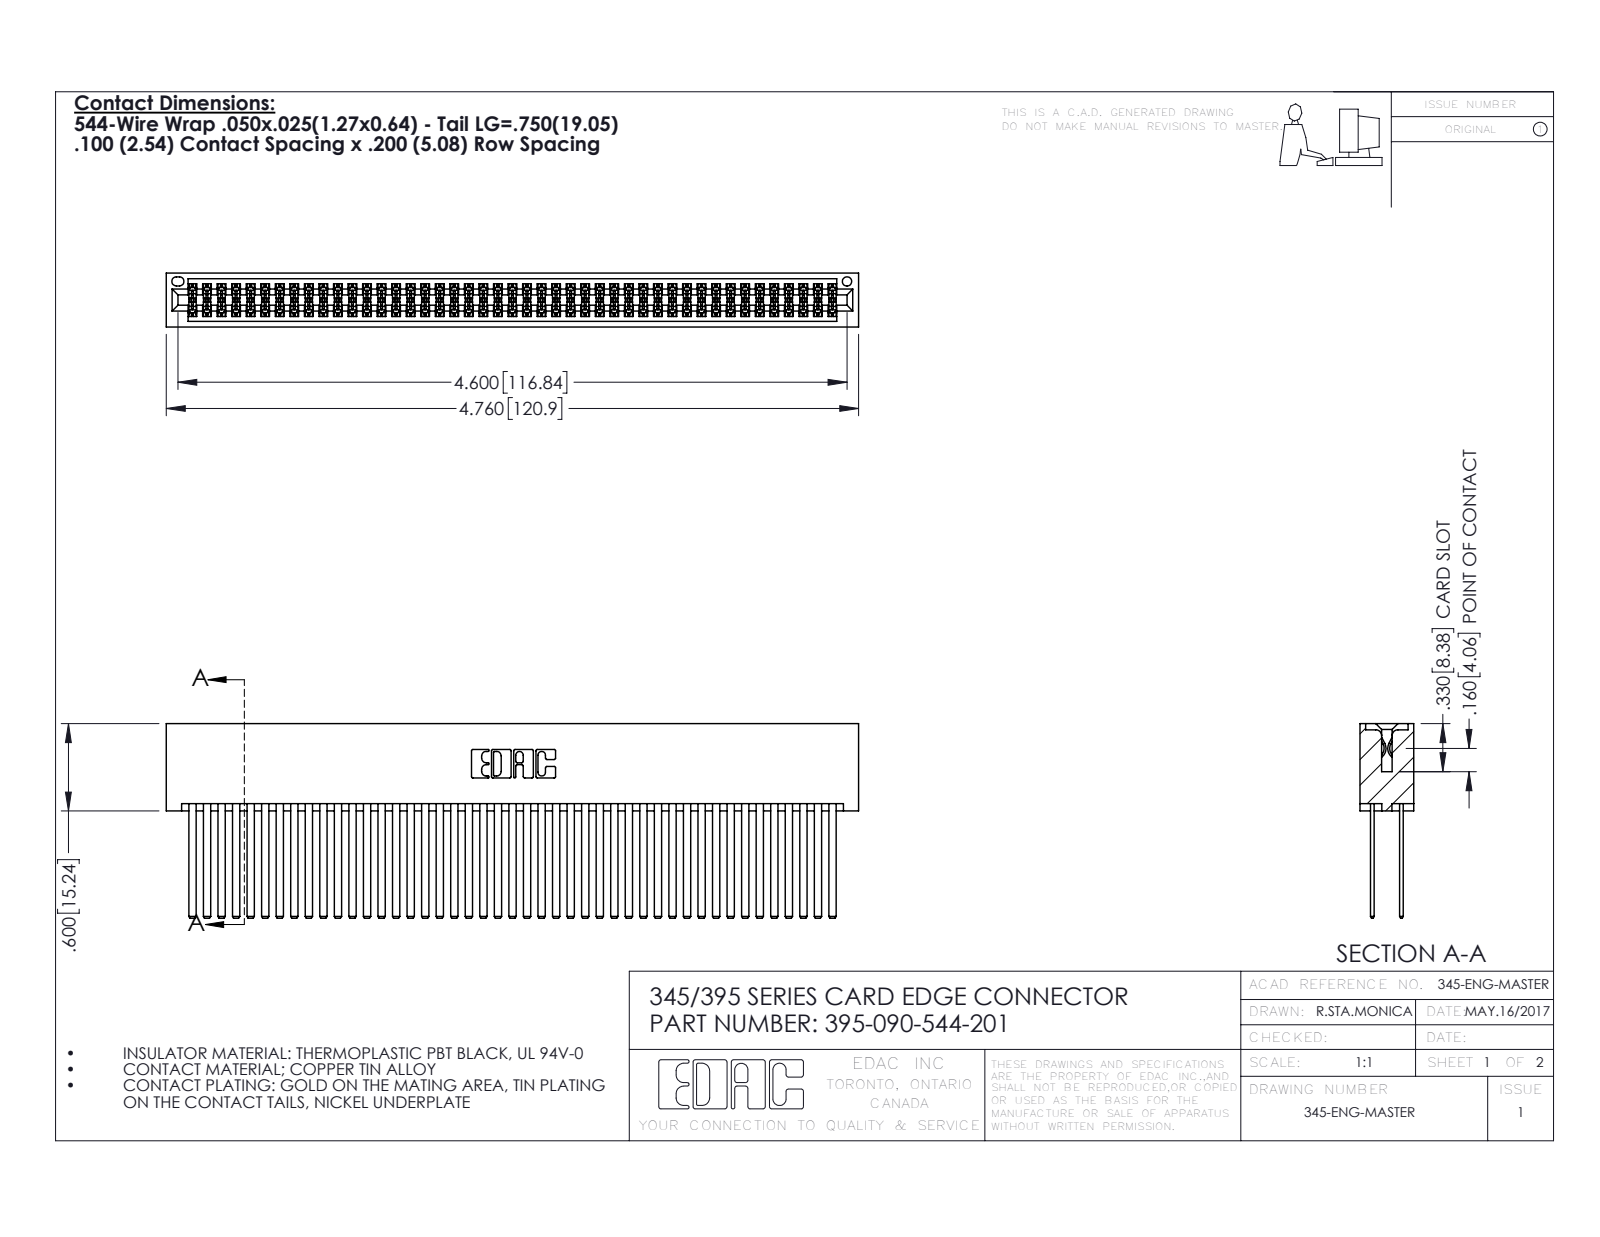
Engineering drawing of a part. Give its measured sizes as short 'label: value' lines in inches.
name: 345-292-001_345-293-144; 395-090-544-201; 345 Part_No Mounting Lugs
written by: SolidWorks 2016 (CONFIG_CONTROL_DESIGN)
unit: in
bodies: 91 solids, 4078 faces (2686 planar, 1392 cylindrical, 0 other)
size: 4.76 × 1.337 × 0.37
volume: 0.833 in³; area: 37.57 in²
holes: 1× ⌀0.064
rounds: 135× R0.006, 22× R0.01, 6× R0.007, 6× R0.031, 3× R0.026, 2× R0.014, 2× R0.019, 2× R0.022
face distances: 0.2, 0.025, 0.298, 0.072, 0.098, 0.272, 0.225, 0.175, 0.37, 0.05
